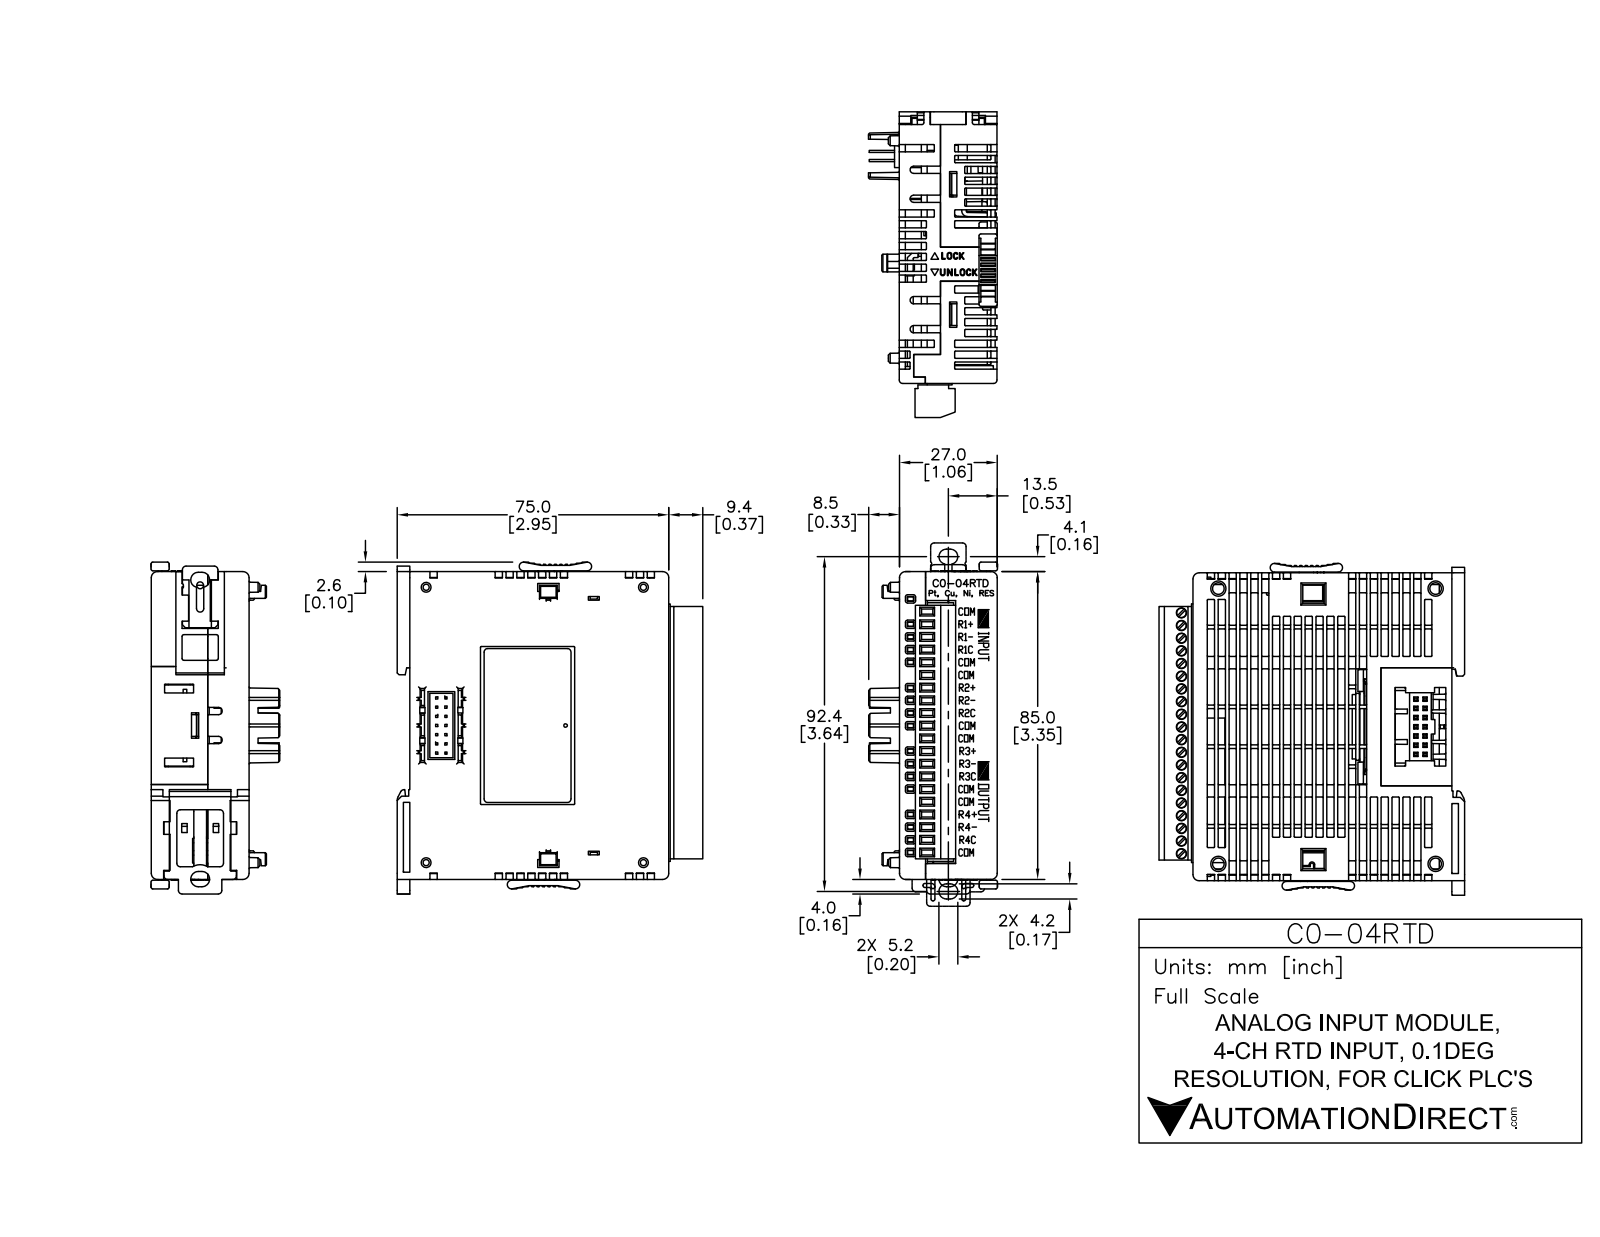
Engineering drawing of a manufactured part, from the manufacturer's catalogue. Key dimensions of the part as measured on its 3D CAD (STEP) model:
Part name (STEP PRODUCT): C0-04RTD
STEP written by: SolidWorks 2013 (AUTOMOTIVE_DESIGN)
Units: millimetres
Bodies: 1 solid, 4085 faces (2893 planar, 1037 cylindrical, 155 other)
Overall size (bounding box): 91.6 × 84.4 × 35.55
Volume: 165 092 mm³ · Surface area: 33 637 mm²
Round holes (diameter × count): ⌀1 ×20, ⌀2.8 ×20, ⌀3.2 ×4, ⌀2 ×2
Round bosses / shafts (diameter × count): ⌀2.6 ×20, ⌀1.9 ×1
Partial cylindrical surfaces — rounded edges, fillets, slot ends (radius × count): R0.2 ×570, R0.5 ×43, R0.3 ×22, R2.8 ×20, R1 ×18, R1.2 ×12, R1.7 ×6, R2.1 ×4
Main face-to-face distances: 0.5, 27.01, 0.51, 26.5, 71.5, 85, 1.7, 26.3, 26.81, 3.5
Hole centre spacings: 3.5, 7, 10.5, 14, 17.5, 21, 24.5, 28
